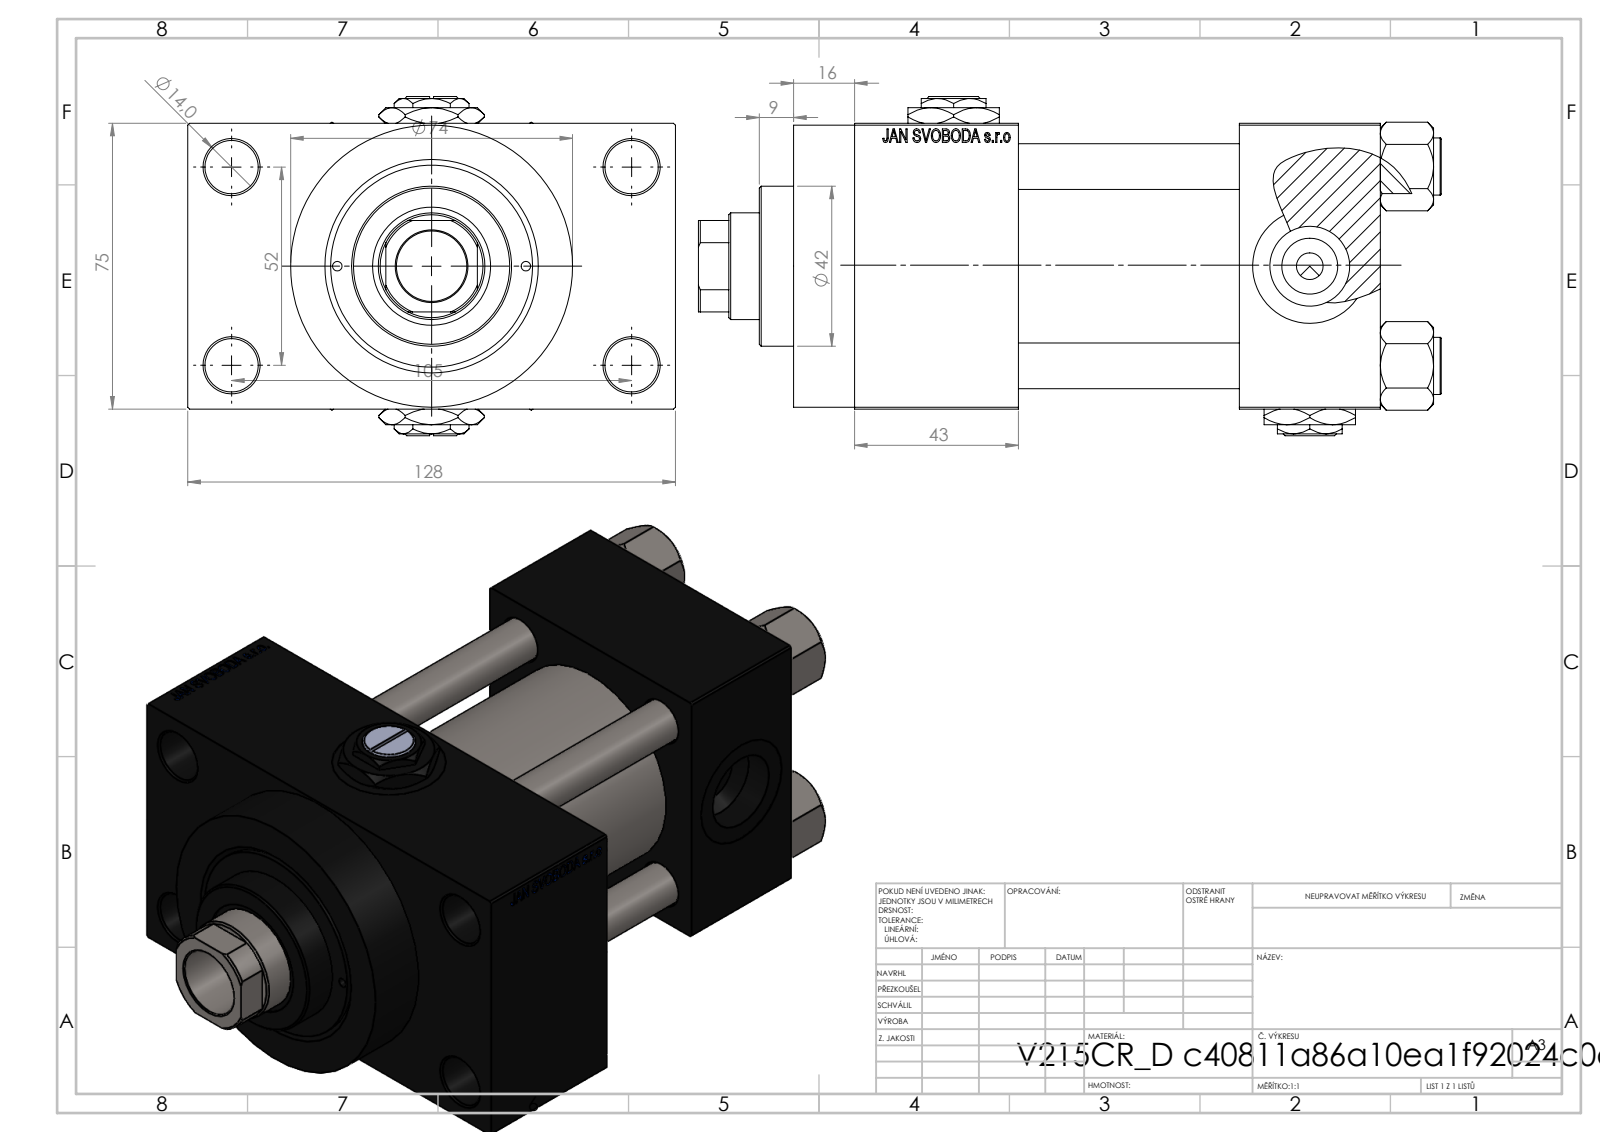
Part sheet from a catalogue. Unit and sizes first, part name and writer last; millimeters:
Units: millimetres
Overall size (bounding box): 195 × 128 × 89
Round holes (diameter × count): ⌀12 ×4, ⌀14 ×4, ⌀7 ×3, ⌀20.96 ×3, ⌀30 ×3, ⌀2.5 ×2, ⌀18.5 ×1, ⌀28 ×1, ⌀31 ×1, ⌀41 ×1, ⌀50 ×1, ⌀53 ×1
Round bosses / shafts (diameter × count): ⌀15 ×4, ⌀74 ×1, ⌀56 ×1, ⌀42 ×1
Partial cylindrical surfaces — rounded edges, fillets, slot ends (radius × count): R13.5 ×1
Main face-to-face distances: 75, 58, 37, 95, 101.5, 26.5, 138, 101, 43, 16
Hole centre spacings: 26.19, 26.35, 36.98, 38.03, 52.3, 57.22, 58.43, 58.59
Volume: 816 079 mm³ · Surface area: 172 755 mm²
Bodies: 13 solids, 1206 faces (545 planar, 99 cylindrical, 562 other)
Part name (STEP PRODUCT): V215CR_D_Body; V215CR_VCP_D; V215_VC_A; NUT_M5_D (+2 more)
STEP written by: SolidWorks 2019 (CONFIG_CONTROL_DESIGN)
